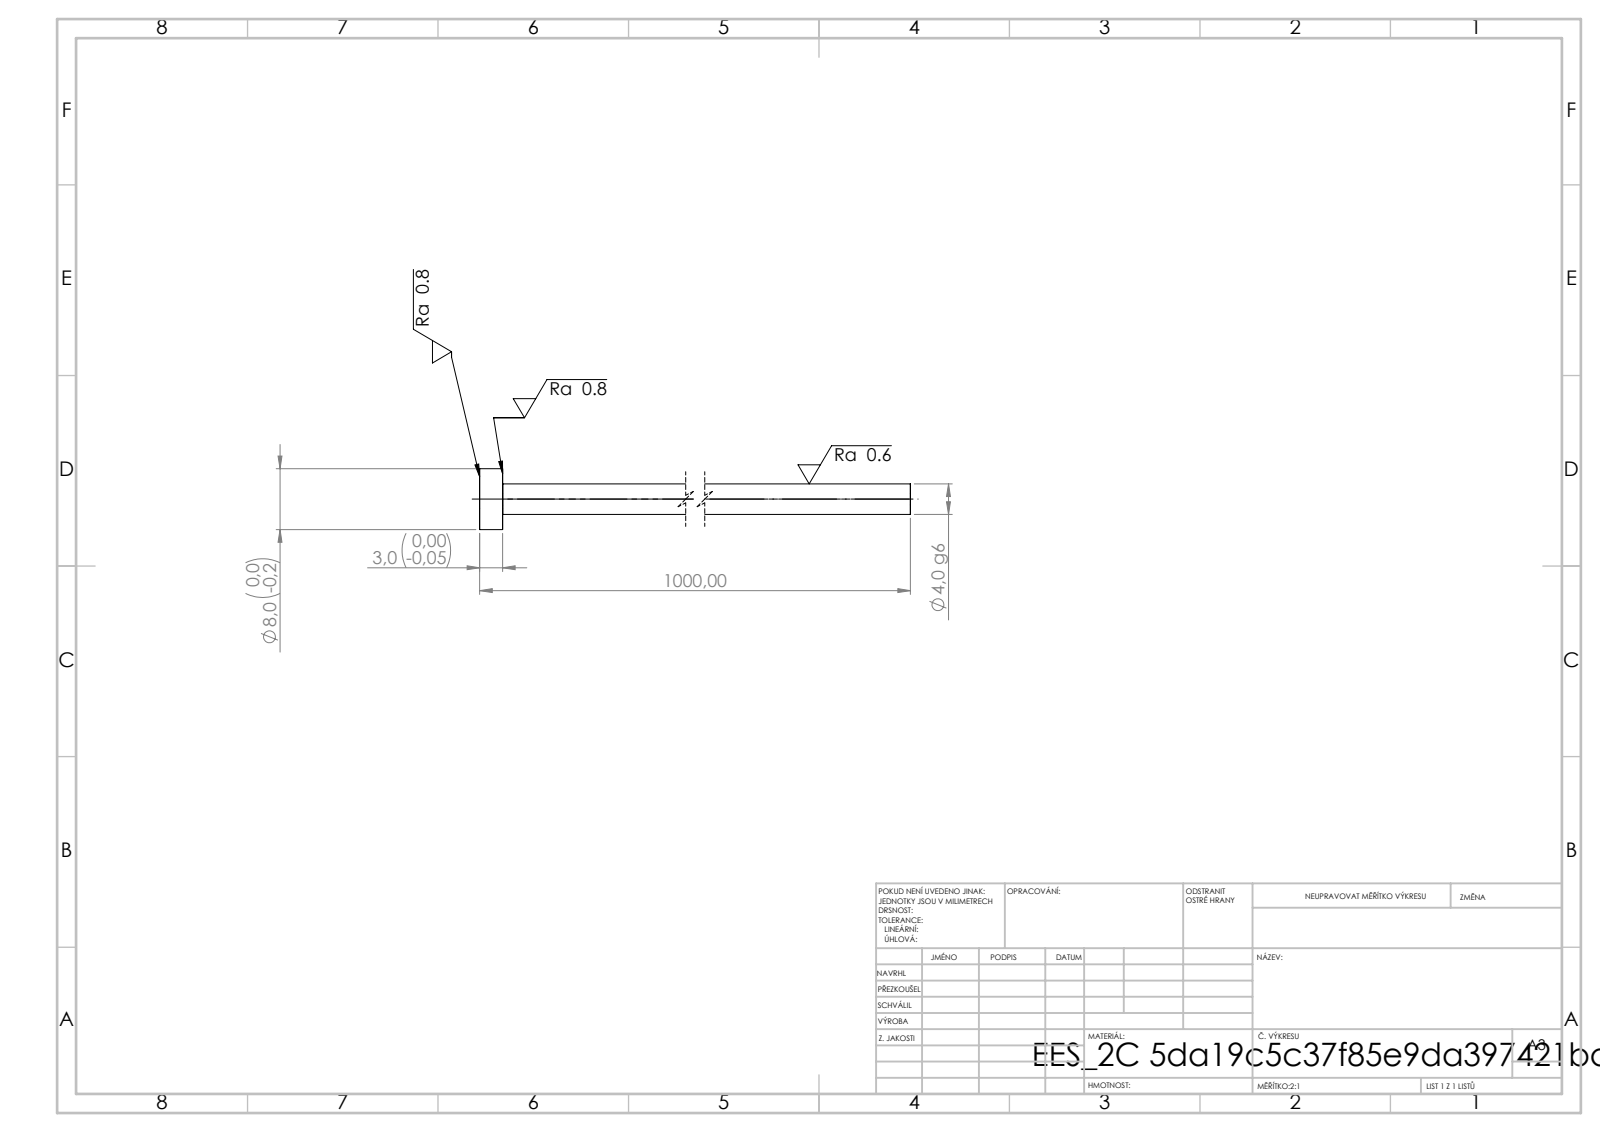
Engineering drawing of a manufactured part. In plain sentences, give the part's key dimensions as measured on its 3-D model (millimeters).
Its 3-D file was written by "SolidWorks 2019 (CONFIG_CONTROL_DESIGN)". It is 1 solid with 7 faces: 3 planar, 4 cylindrical and 0 other. Overall it measures 1000 by 8 by 8 millimeters. Its volume is 12 679 cubic millimeters and its surface area 12 705 square millimeters. Round bosses or shafts: 1 of diameter 8, 1 of diameter 4. The main face-to-face distances are 3, 1000, 997.
